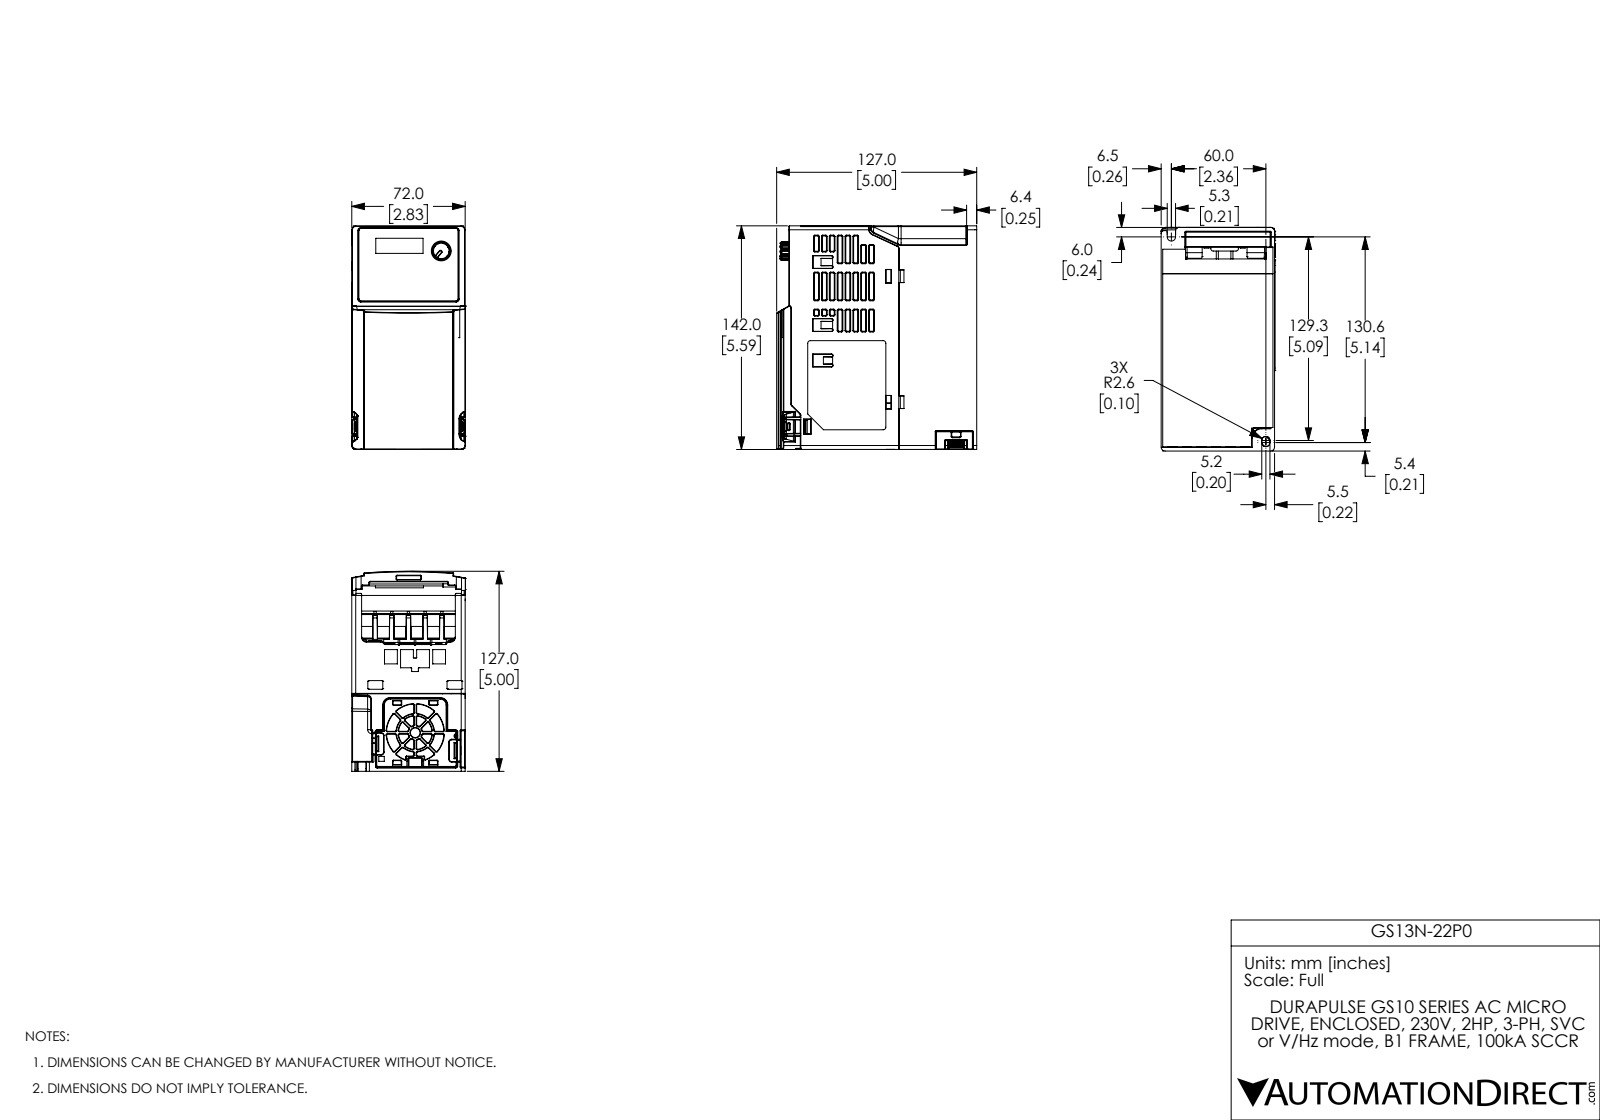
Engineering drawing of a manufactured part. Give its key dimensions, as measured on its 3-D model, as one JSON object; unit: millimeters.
{"part_name": "VFD-ME300-B3-PD-3D00-KEN_ASM REAR CASE n TermB ONLY 1 New 1B r3 COMPLETE 1knob cmb2b mod2 for B1b", "step_written_by": "SolidWorks 2017 (AUTOMOTIVE_DESIGN)", "units": "millimeters", "bodies": {"solids": 8, "faces": 5418, "planar": 2496, "cylindrical": 1660, "other": 1262}, "overall_size": [142.03, 127.02, 72.16], "volume_mm3": 718122, "surface_area_mm2": 171907, "round_holes": [[4.3, 4], [6.1, 1], [10.9, 1], [12.6, 1]], "round_bosses_or_shafts": [[6.8, 4], [4, 4]], "partial_cylinders_radius": [[0.5, 434], [0.3, 222], [1, 54], [0.4, 52], [0.32, 45], [1.5, 16], [0.32, 13], [2, 12]], "face_to_face_distances": [1, 71, 72, 70, 62.2, 0.8, 1.81, 142, 70.81, 8.61], "hole_center_spacings": [10.2, 20.4, 30.6, 115.16, 115.73, 117.19, 119.5]}
